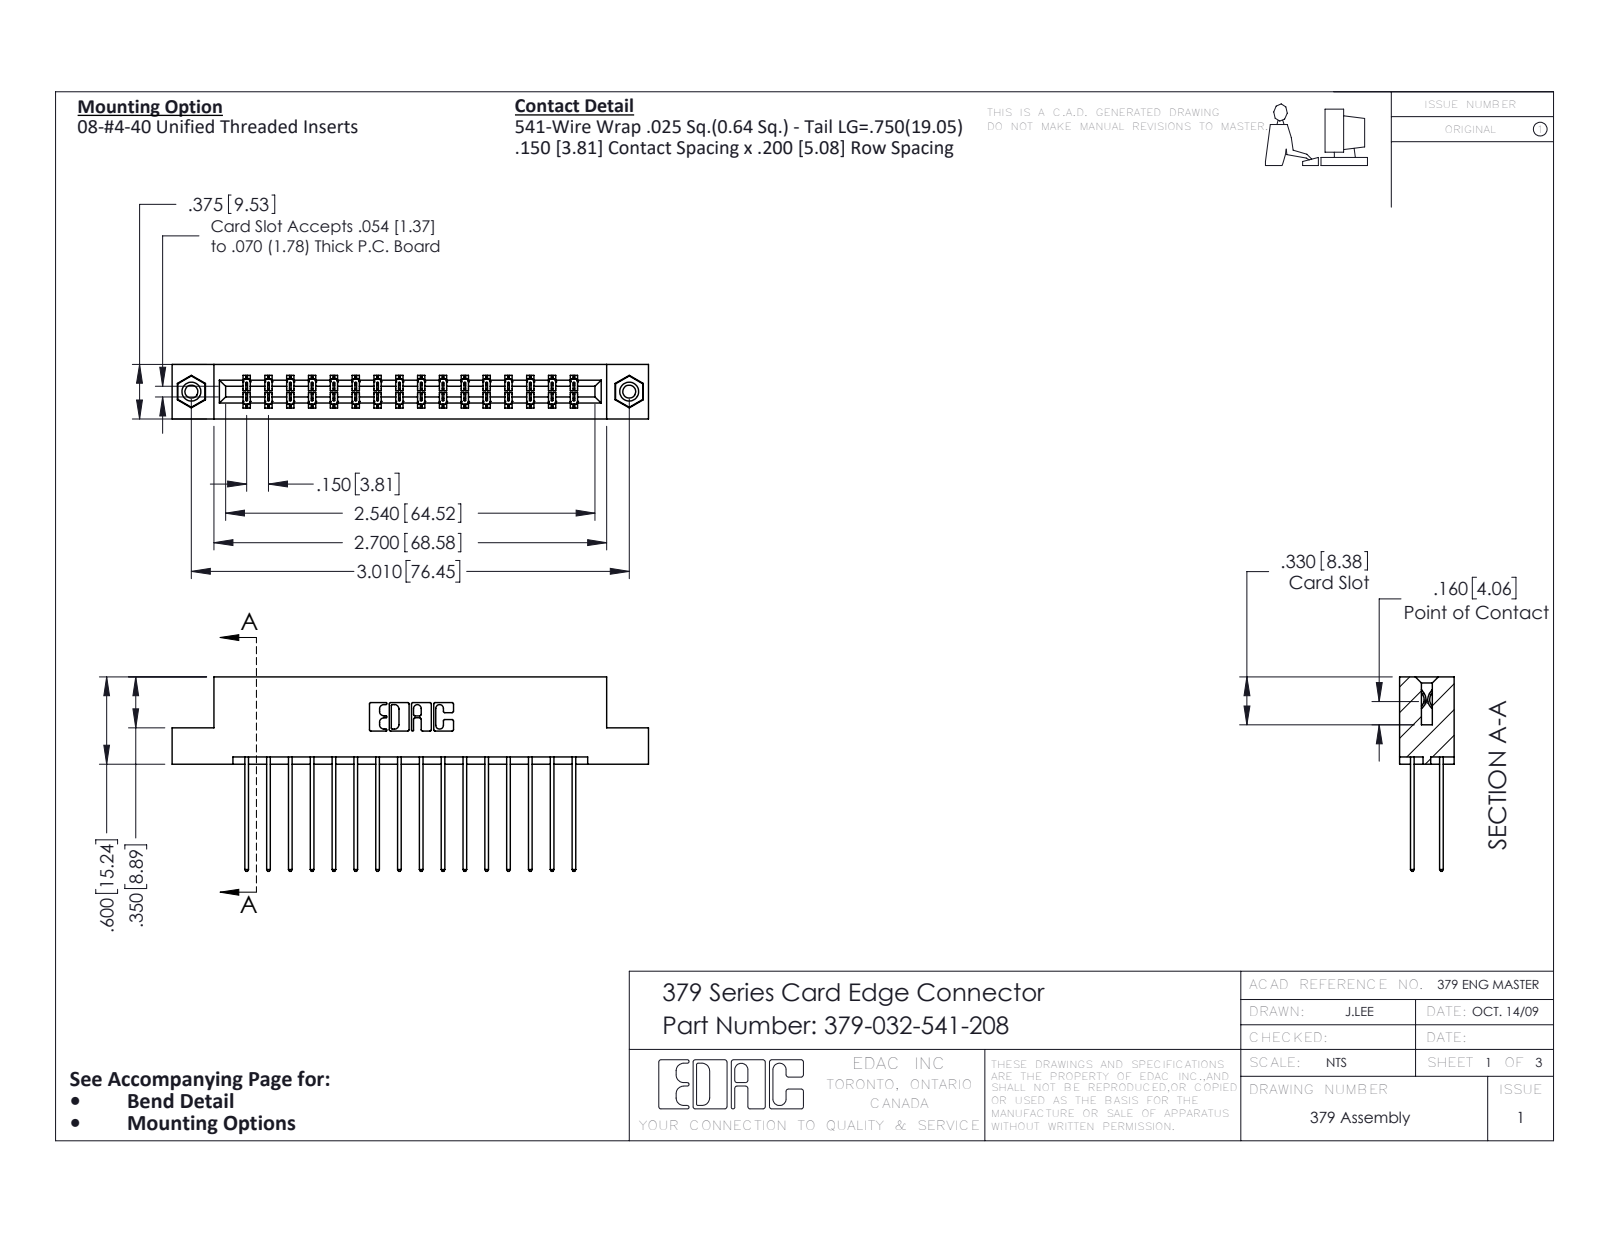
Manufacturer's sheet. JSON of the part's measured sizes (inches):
{"part_name": "379 Part_Flush - .156 Dia - TI; 345-292-001_345-293-141; 345-250-001_345-250-003-102; 379-032-541-208", "step_written_by": "SolidWorks 2020 (CONFIG_CONTROL_DESIGN)", "units": "inches", "bodies": {"solids": 35, "faces": 1838, "planar": 1254, "cylindrical": 568, "other": 16}, "overall_size": [3.275, 1.337, 0.375], "volume_in3": 0.532, "surface_area_in2": 16.26, "round_holes": [[0.089, 2], [0.125, 2], [0.156, 2]], "round_bosses_or_shafts": [[0.155, 2]], "partial_cylinders_radius": [[0.006, 63], [0.01, 32], [0.01, 22], [0.007, 6], [0.031, 6], [0.026, 3], [0.014, 2], [0.022, 2]], "face_to_face_distances": [0.3, 0.075, 0.2, 0.1, 0.375, 0.275, 0.15, 0.025, 0.05, 0.6], "hole_center_spacings": [3.01]}
